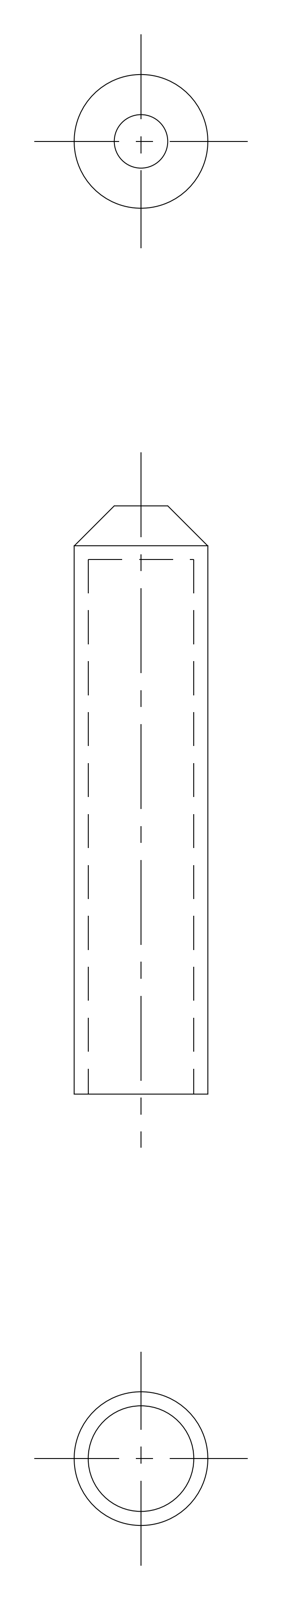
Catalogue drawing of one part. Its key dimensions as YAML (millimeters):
part_name: "67109426"
step_written_by: "CADfix (AUTOMOTIVE_DESIGN)"
units: millimeters
bodies: {solids: 1, faces: 9, planar: 0, cylindrical: 0, other: 9}
overall_size: [44, 10, 10]
volume: 1386
surface_area: 2469
